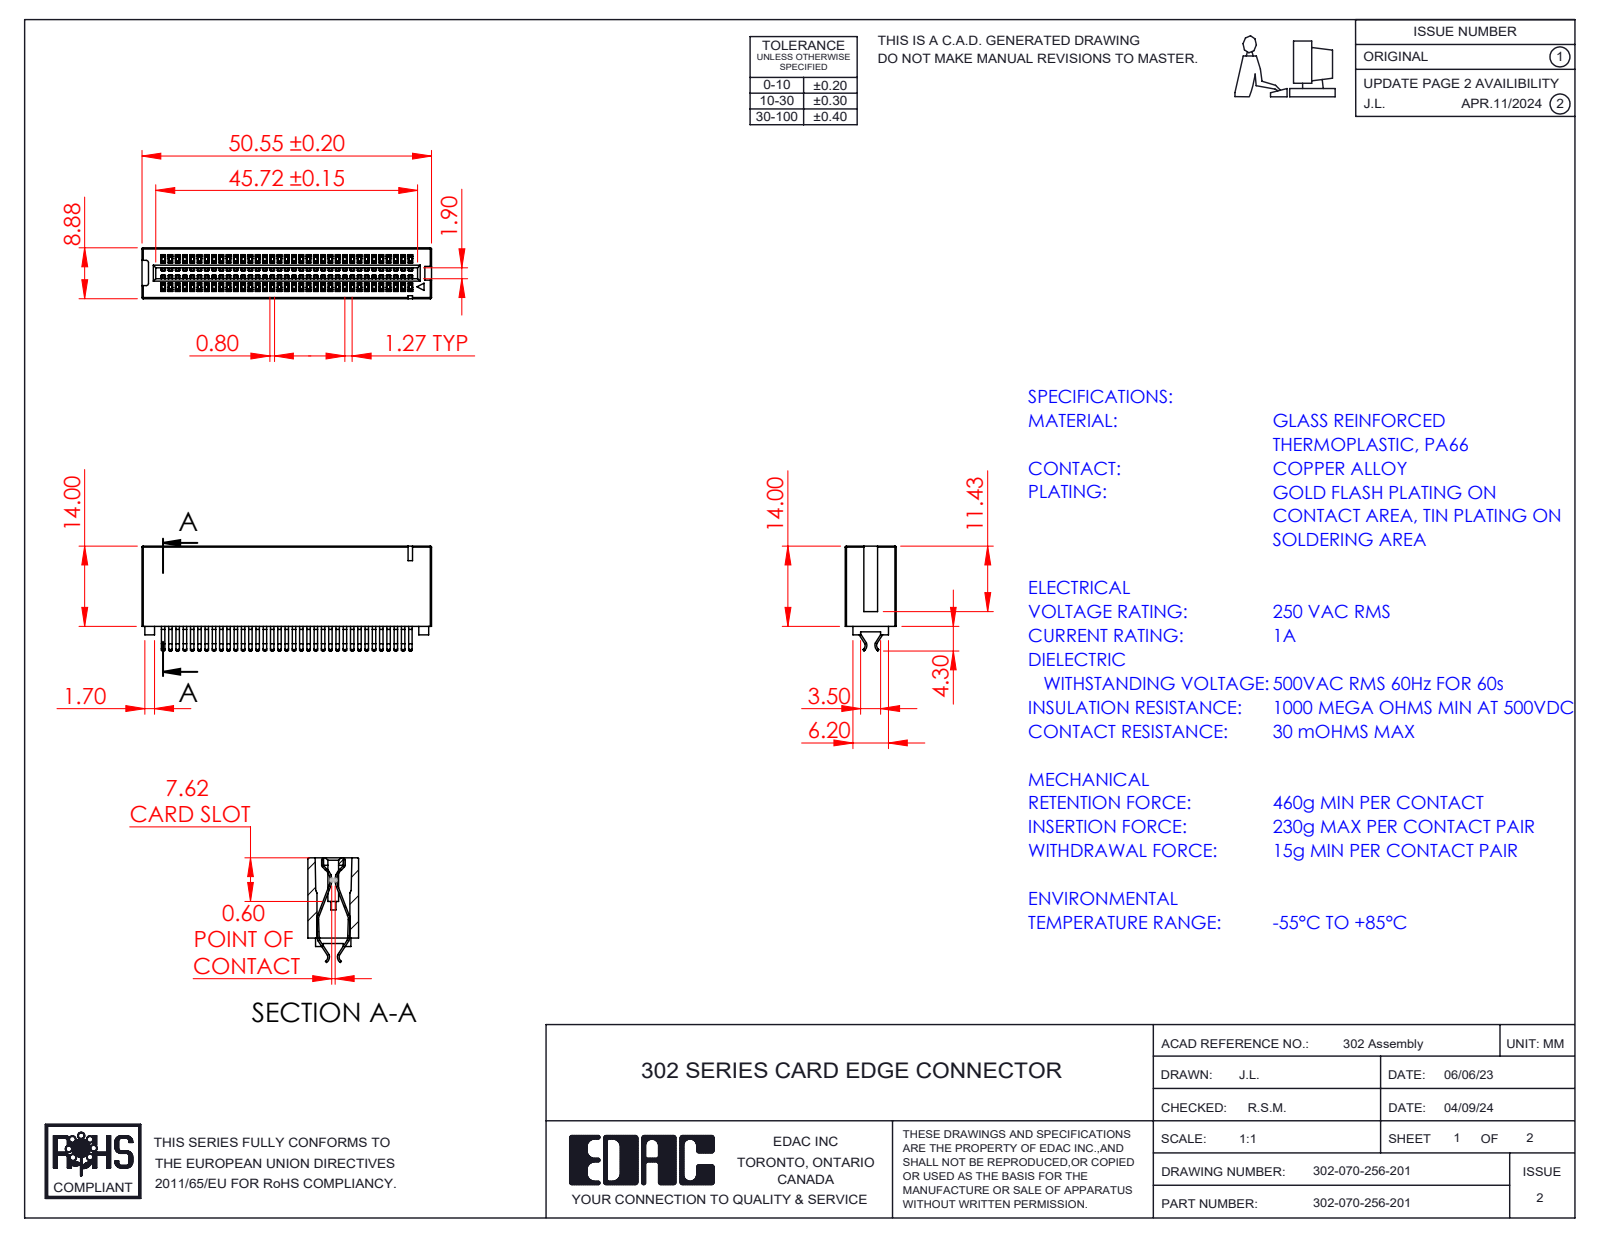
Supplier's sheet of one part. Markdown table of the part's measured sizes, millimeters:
| quantity | value |
| --- | --- |
| part name | Contact_302-290-X56; 302-070-256-201; HSG_Vertical HSG |
| STEP written by | SolidWorks 2023 (CONFIG_CONTROL_DESIGN) |
| units | millimeters |
| bodies | 71 solids, 3391 faces (2254 planar, 1133 cylindrical, 4 other) |
| overall size | 50.55 × 18.3 × 8.88 |
| volume | 3 941 mm³ |
| surface area | 10 855 mm² |
| partial cylindrical surfaces (radius × count) | 0.2 × 218, 0.11 × 2, 0.4 × 2, 0.41 × 2, 0.93 × 2, 1.05 × 2, 1.23 × 2, 1.25 × 2 |
| main face-to-face distances | 1.27, 2.54, 3.81, 5.08, 6.35, 7.62, 8.88, 8.89, 10.16, 11.43 |
